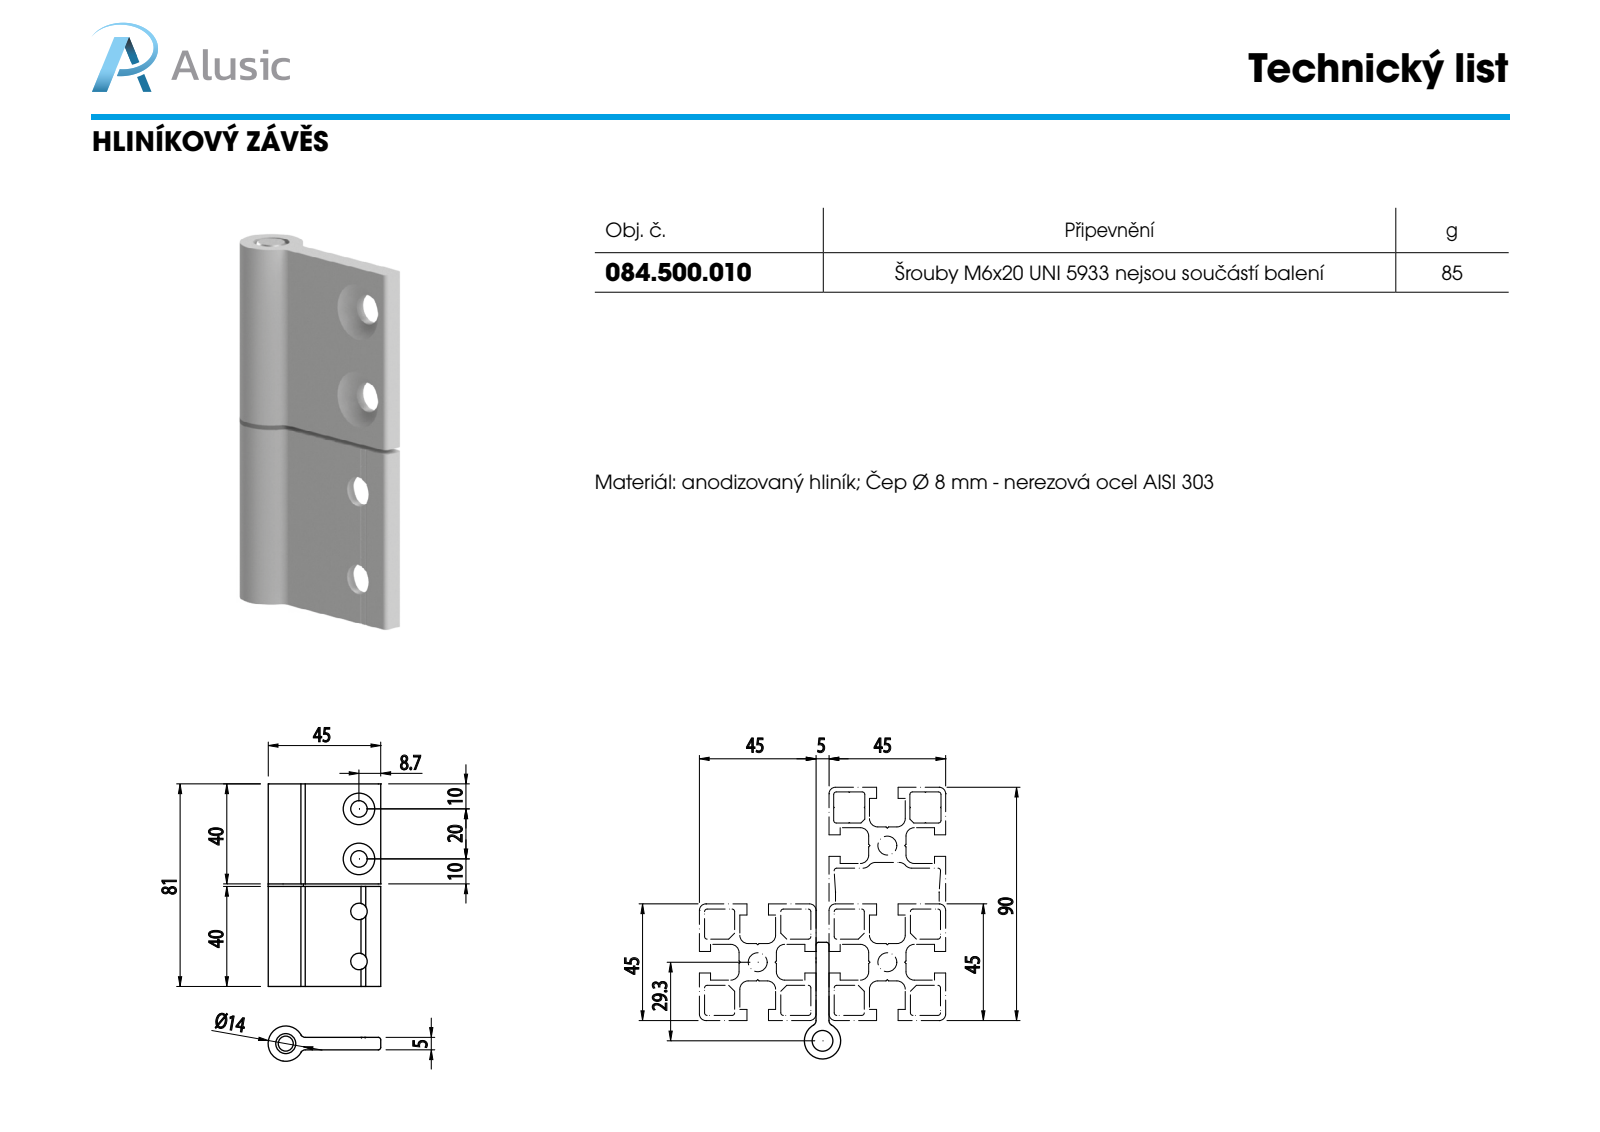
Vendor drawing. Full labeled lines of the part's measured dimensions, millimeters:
Part name (STEP PRODUCT): 084.500.010; 084.500.001.C; PERNO CERNIERA_084.500.001.B; 084.500.010L
STEP written by: SolidWorks 2011 (CONFIG_CONTROL_DESIGN)
Units: millimetres
Bodies: 4 solids, 204 faces (154 planar, 38 cylindrical, 12 other)
Overall size (bounding box): 81 × 45.05 × 14.1
Volume: 23 728 mm³ · Surface area: 13 968 mm²
Round holes (diameter × count): ⌀6.6 ×4, ⌀8 ×1, ⌀8.1 ×1
Round bosses / shafts (diameter × count): ⌀14.1 ×1, ⌀14 ×1
Partial cylindrical surfaces — rounded edges, fillets, slot ends (radius × count): R0.2 ×2, R1 ×2, R2 ×2
Main face-to-face distances: 5, 40, 41, 1, 81, 6.11, 6.12, 3.26, 34.5, 5.5
Hole centre spacings: 20, 41, 21, 61
